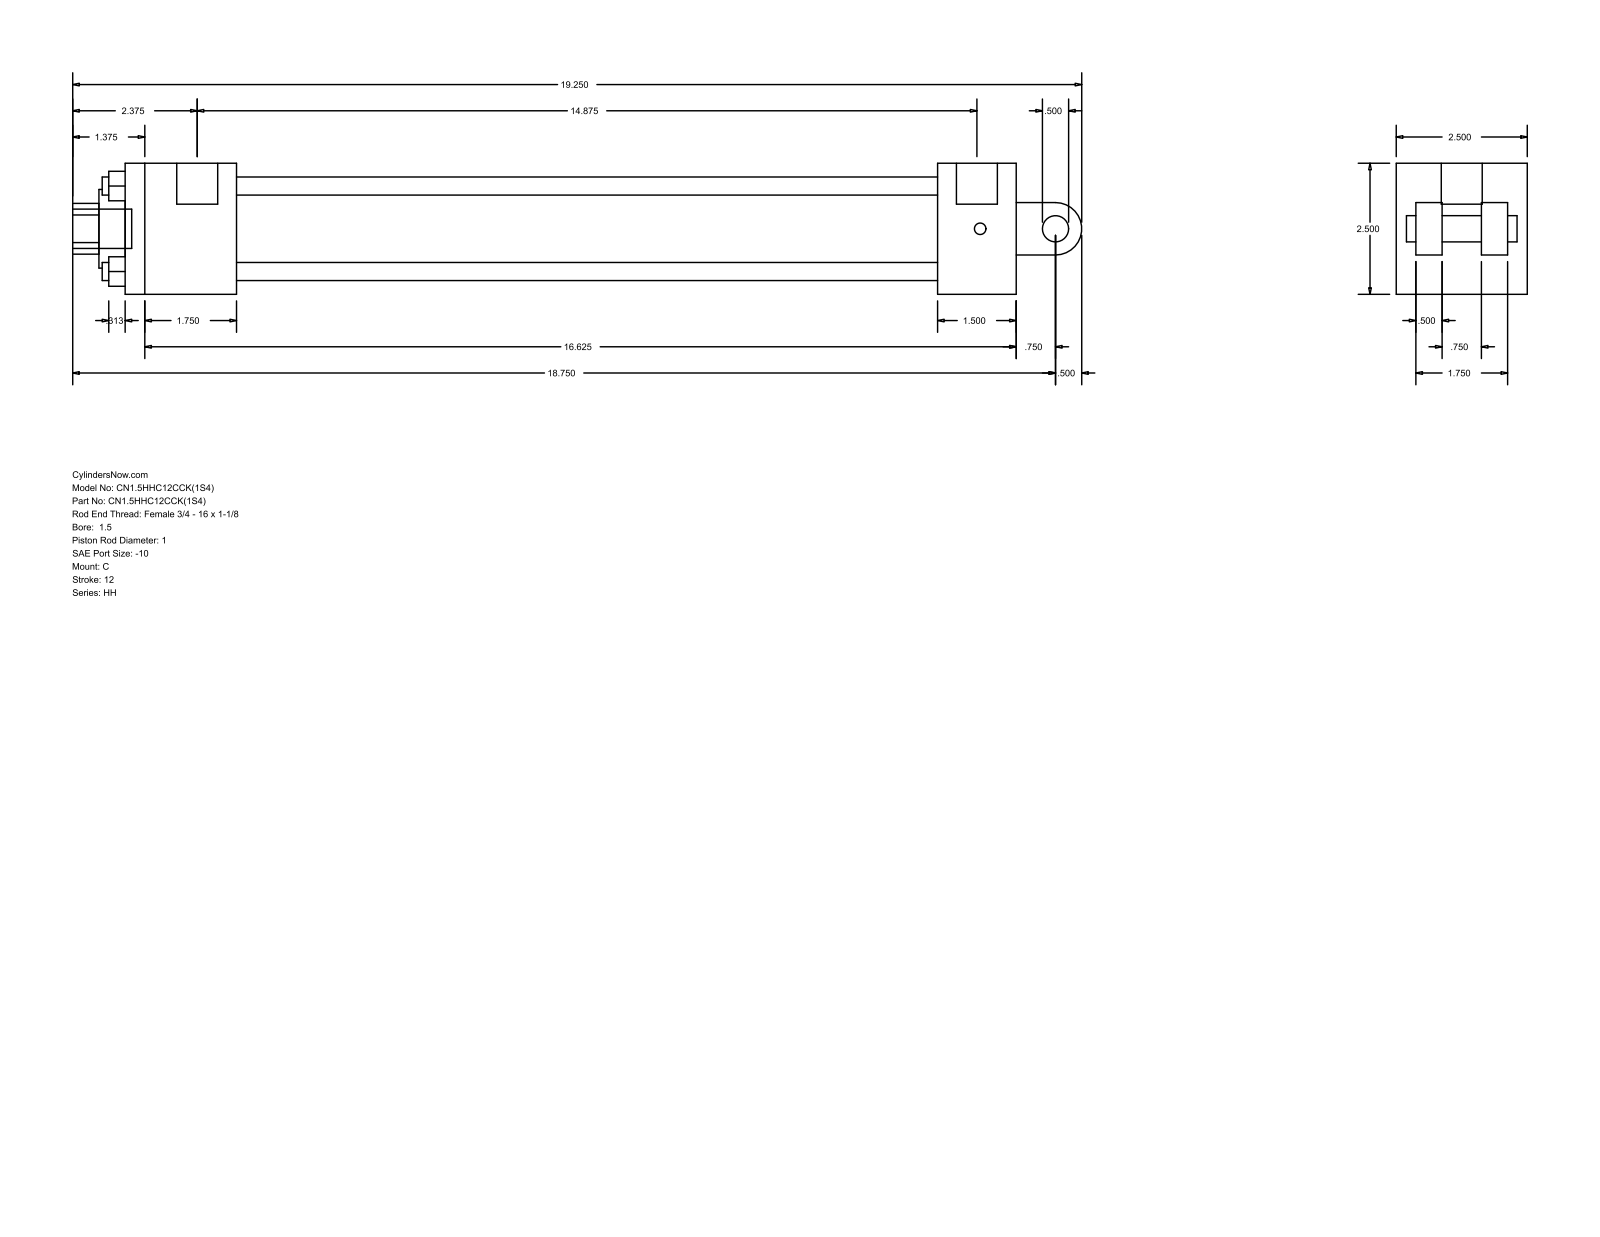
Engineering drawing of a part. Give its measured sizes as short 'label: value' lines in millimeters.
name: HH_C__0150_1
written by: GSSL Pune (CONFIG_CONTROL_DESIGN)
unit: mm
bodies: 0 solids, 99 faces (70 planar, 29 cylindrical, 0 other)
size: 488.95 × 63.5 × 63.5
holes: 4× ⌀8.76, 2× ⌀5.56, 1× ⌀19.84, 1× ⌀25.4, 1× ⌀38.1, 1× ⌀44.45
bosses: 2× ⌀5.56, 1× ⌀19.84, 1× ⌀19.05, 1× ⌀12.7
rounds: 1× R12.29, 1× R12.7
face distances: 63.5, 53.98, 339.72, 377.82, 38.1, 393.7, 431.8, 12.7, 22.22, 41.28
hole spacings: 29.27, 41.4, 58.55, 1.59
